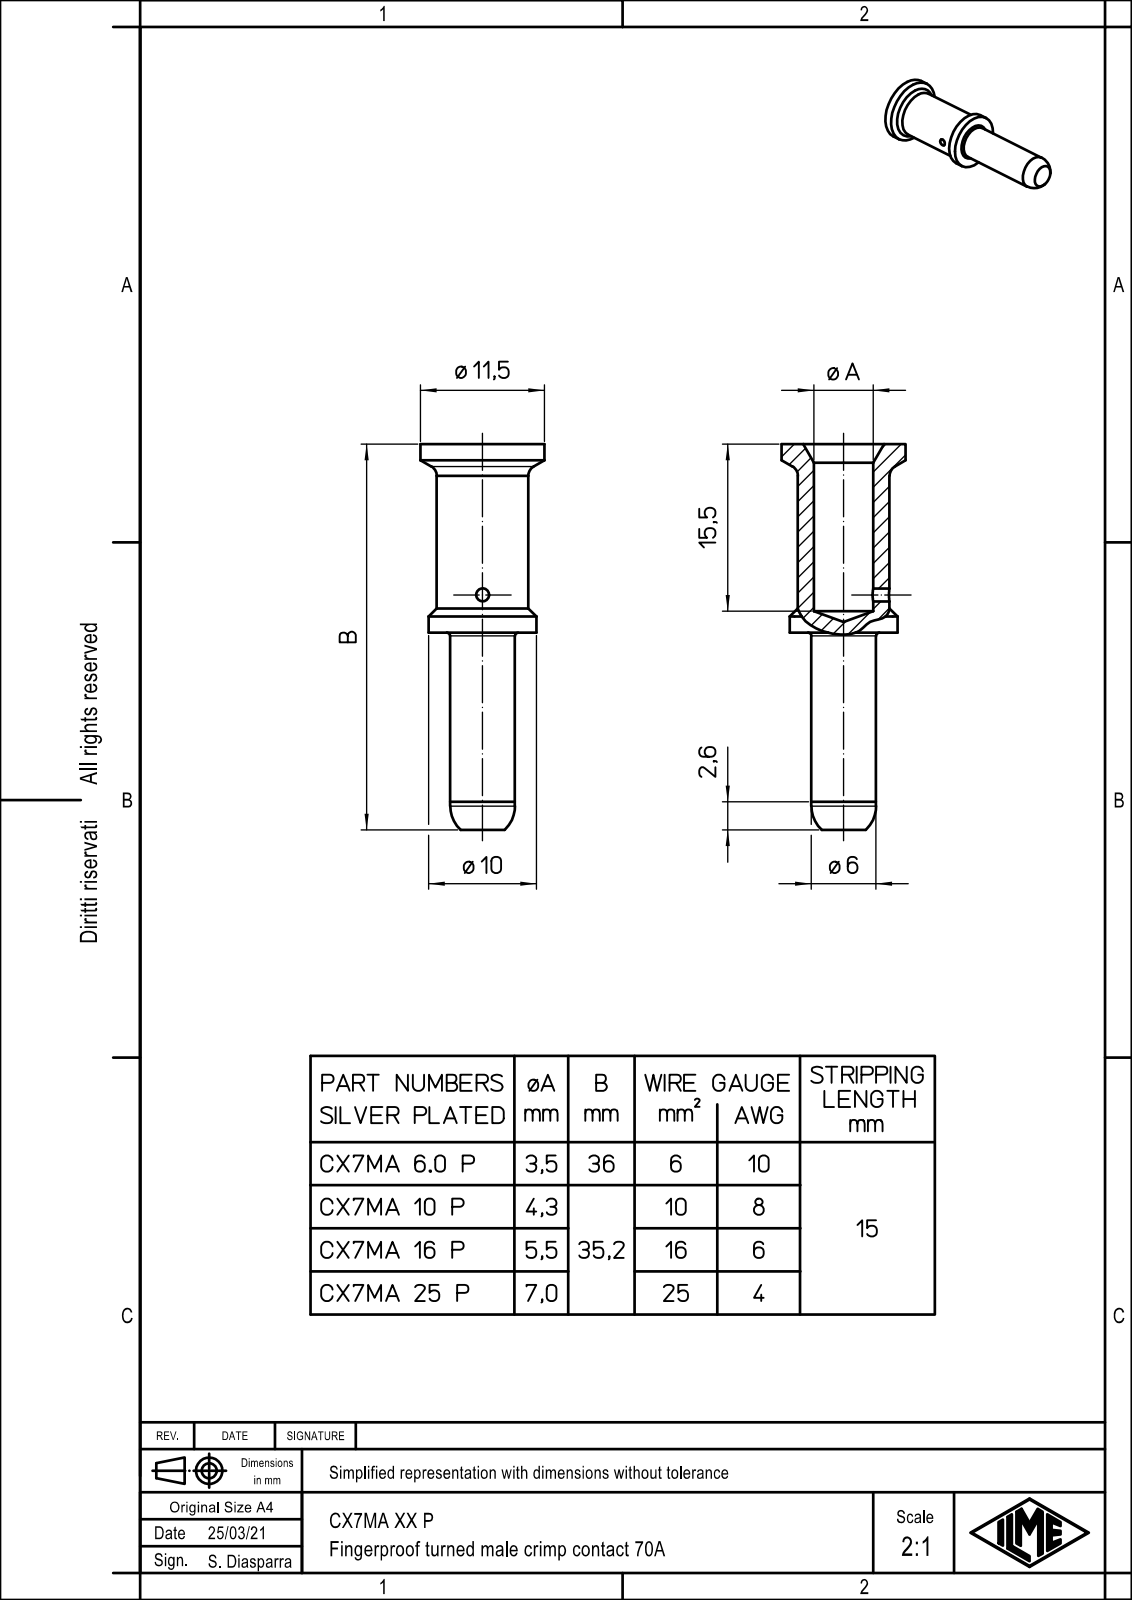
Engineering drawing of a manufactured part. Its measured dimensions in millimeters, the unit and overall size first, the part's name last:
Units: millimetres
Overall size (bounding box): 36.6 × 11.5 × 11.5
Round holes (diameter × count): ⌀1.2 ×1, ⌀3.5 ×1
Round bosses / shafts (diameter × count): ⌀11.5 ×1, ⌀10 ×1, ⌀6.5 ×1, ⌀6 ×1
Main face-to-face distances: 18, 36.6, 18.6, 34, 16, 2.6
Volume: 1 189 mm³ · Surface area: 1 179 mm²
Bodies: 1 solid, 30 faces (4 planar, 14 cylindrical, 12 other)
Part name (STEP PRODUCT): CX7MA 6.0 P
STEP written by: Creo Elements/Direct Modeling 20.1B 02-Apr-2019 (C) Parametric Technology GmbH (AUTOMOTIVE_DESIGN)
